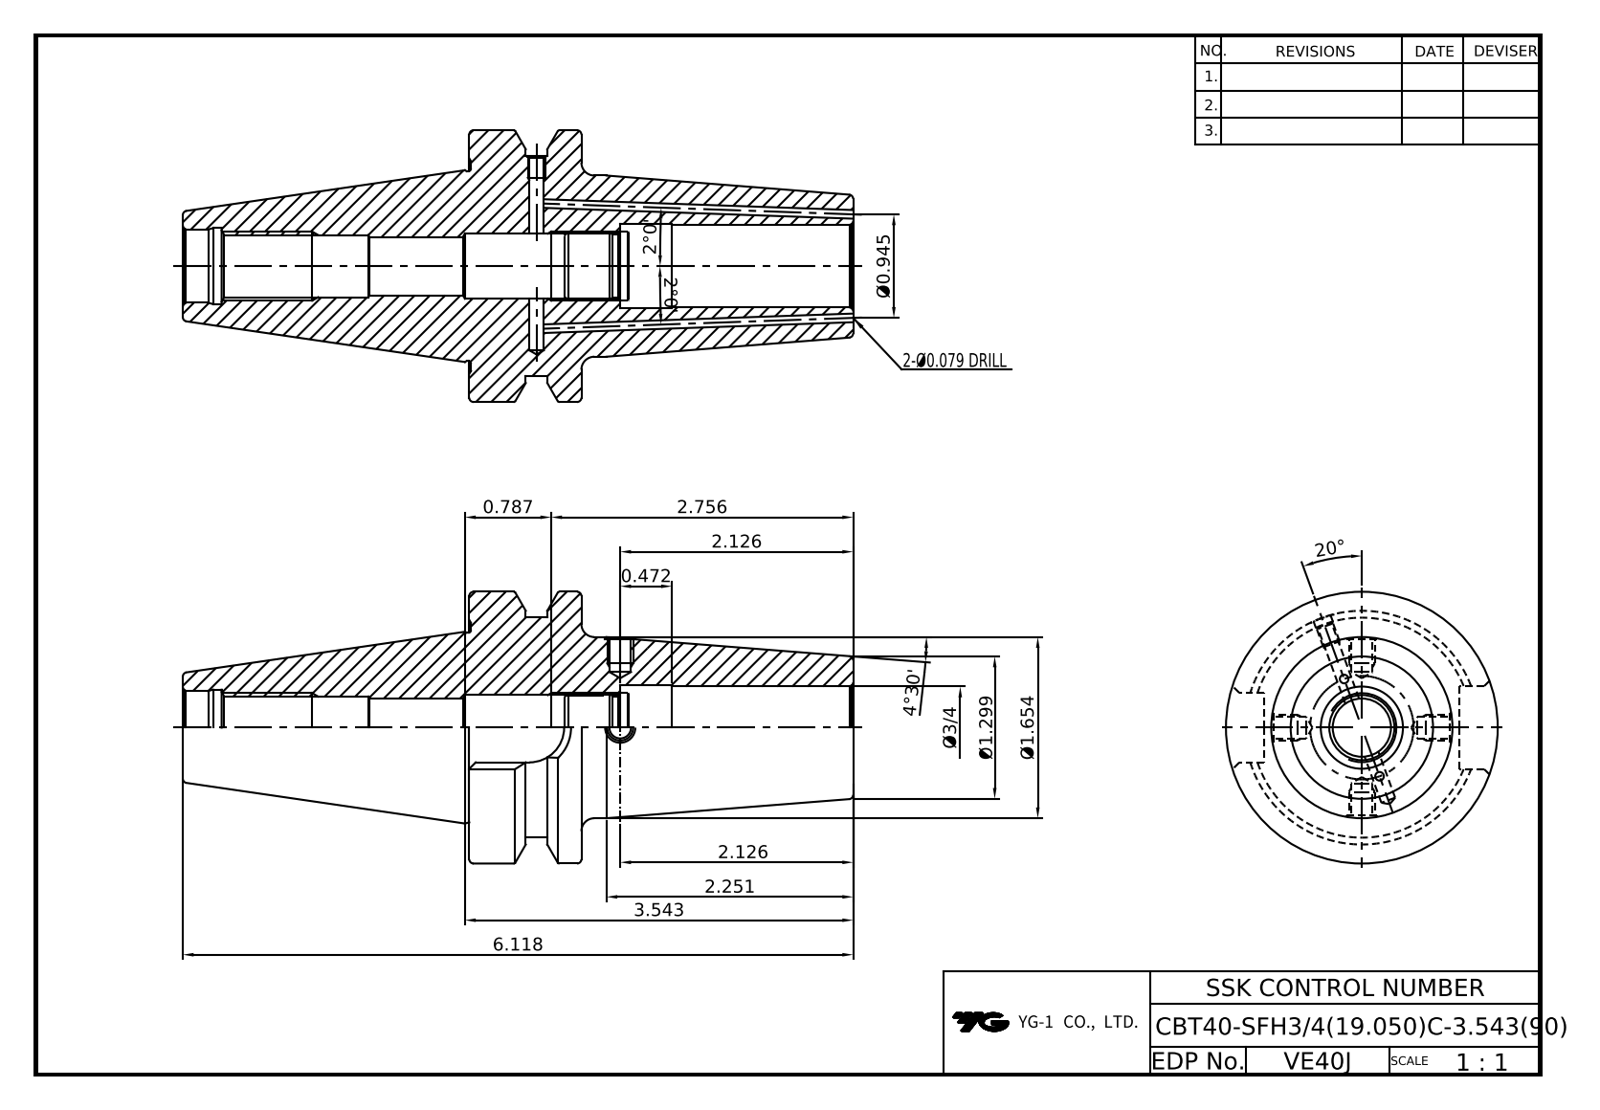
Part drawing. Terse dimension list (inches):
name: CBT40-SFH19_05C-90
written by: CREO PARAMETRIC BY PTC INC, 2018500 (CONFIG_CONTROL_DESIGN)
unit: in
bodies: 1 solid, 88 faces (22 planar, 26 cylindrical, 40 other)
size: 6.118 × 2.48 × 2.48
volume: 10.61 in³; area: 52.9 in²
holes: 1× ⌀0.531, 1× ⌀0.551, 1× ⌀0.63, 1× ⌀0.669, 1× ⌀0.693, 1× ⌀0.75, 1× ⌀0.774
bosses: 1× ⌀2.48, 1× ⌀2.008, 1× ⌀1.732, 1× ⌀1.654
rounds: 1× R0.317
face distances: 0.984, 3.465, 2.48, 1.78, 0.673, 0.311, 2.791, 0.476, 0.197, 0.508
